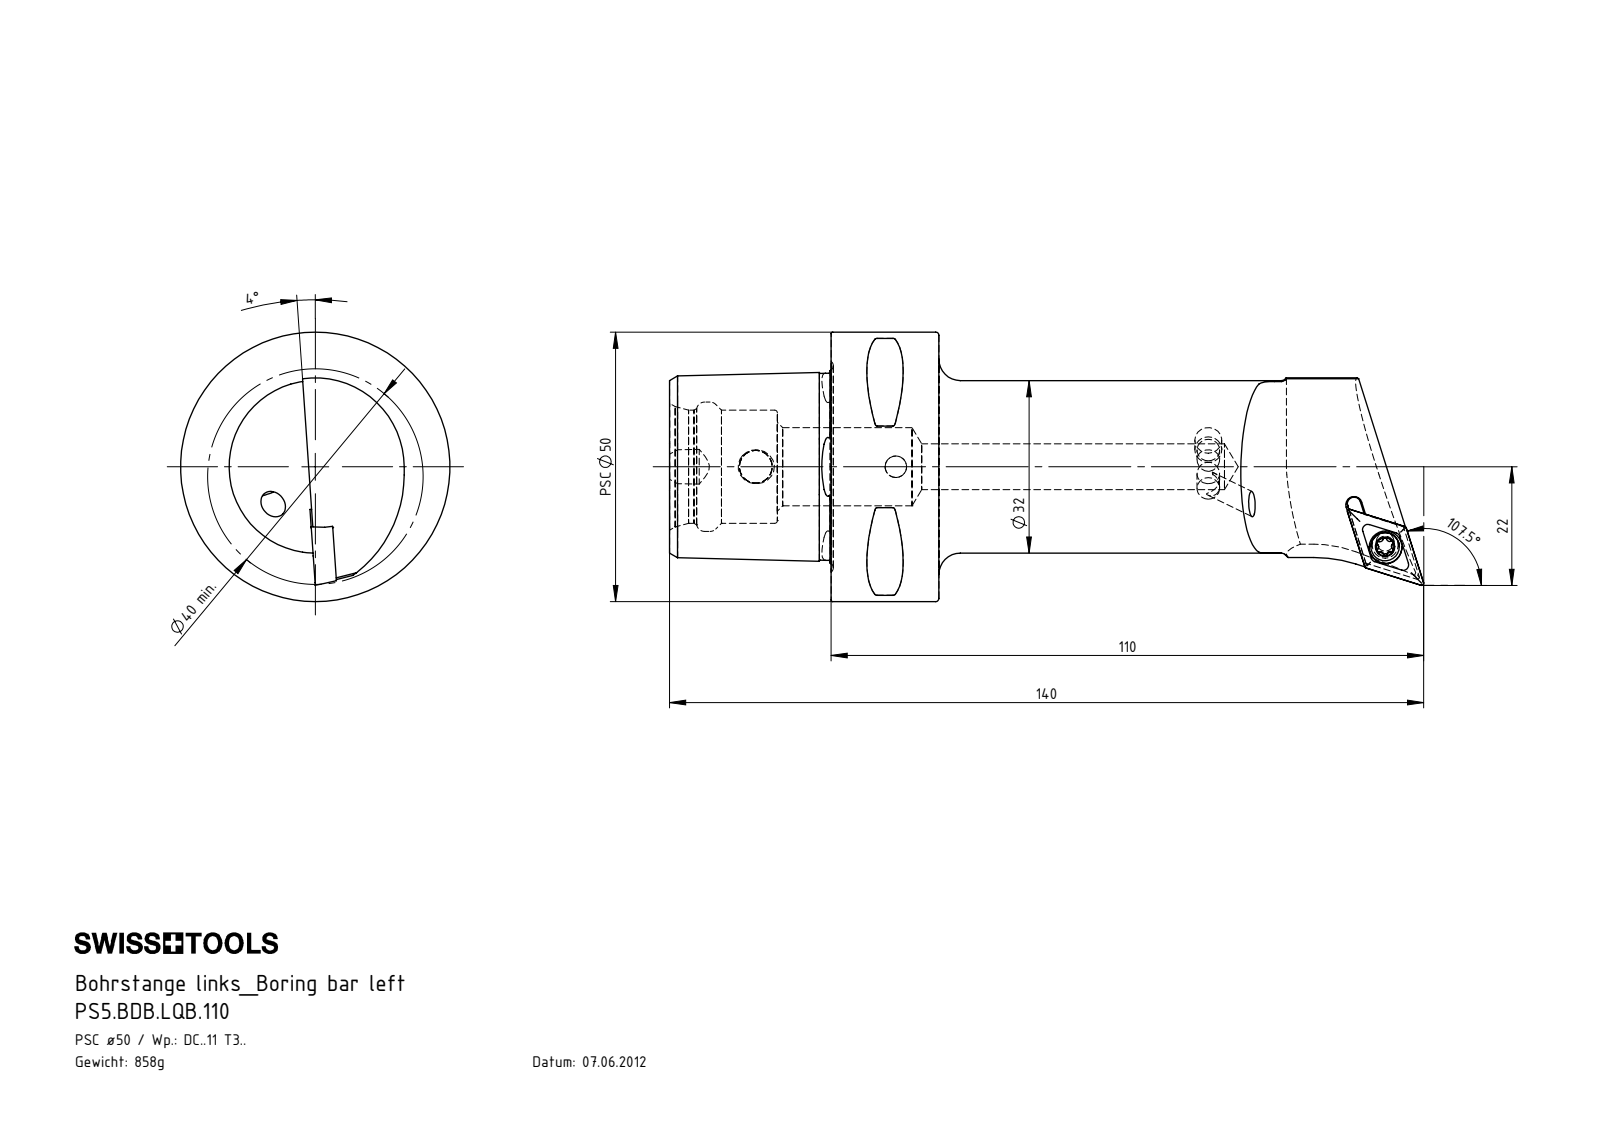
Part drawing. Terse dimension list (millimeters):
name: PS5-BDB.LQB.110_A; PS5.BDB.LQB.110; DCMT11T304; WCB-ER2.001.009_A (+1 more)
written by: SolidWorks 2017 (AUTOMOTIVE_DESIGN)
unit: mm
bodies: 5 solids, 289 faces (53 planar, 75 cylindrical, 161 other)
size: 140 × 50 × 50
volume: 109 020 mm³; area: 23 626 mm²
holes: 2× ⌀4, 2× ⌀4.2, 2× ⌀6.1, 1× ⌀3.3, 1× ⌀4.4, 1× ⌀8.5, 1× ⌀14.5, 1× ⌀21, 1× ⌀24
bosses: 1× ⌀50, 1× ⌀32, 1× ⌀5.25, 1× ⌀5, 1× ⌀4
rounds: 8× R0.5, 6× R0.34, 6× R0.59, 1× R1.25, 1× R3, 1× R4, 1× R16.5, 1× R23
face distances: 20, 30, 50, 19.18, 3.67, 44.4, 10, 29.8, 9.8, 20.2
hole spacings: 26
